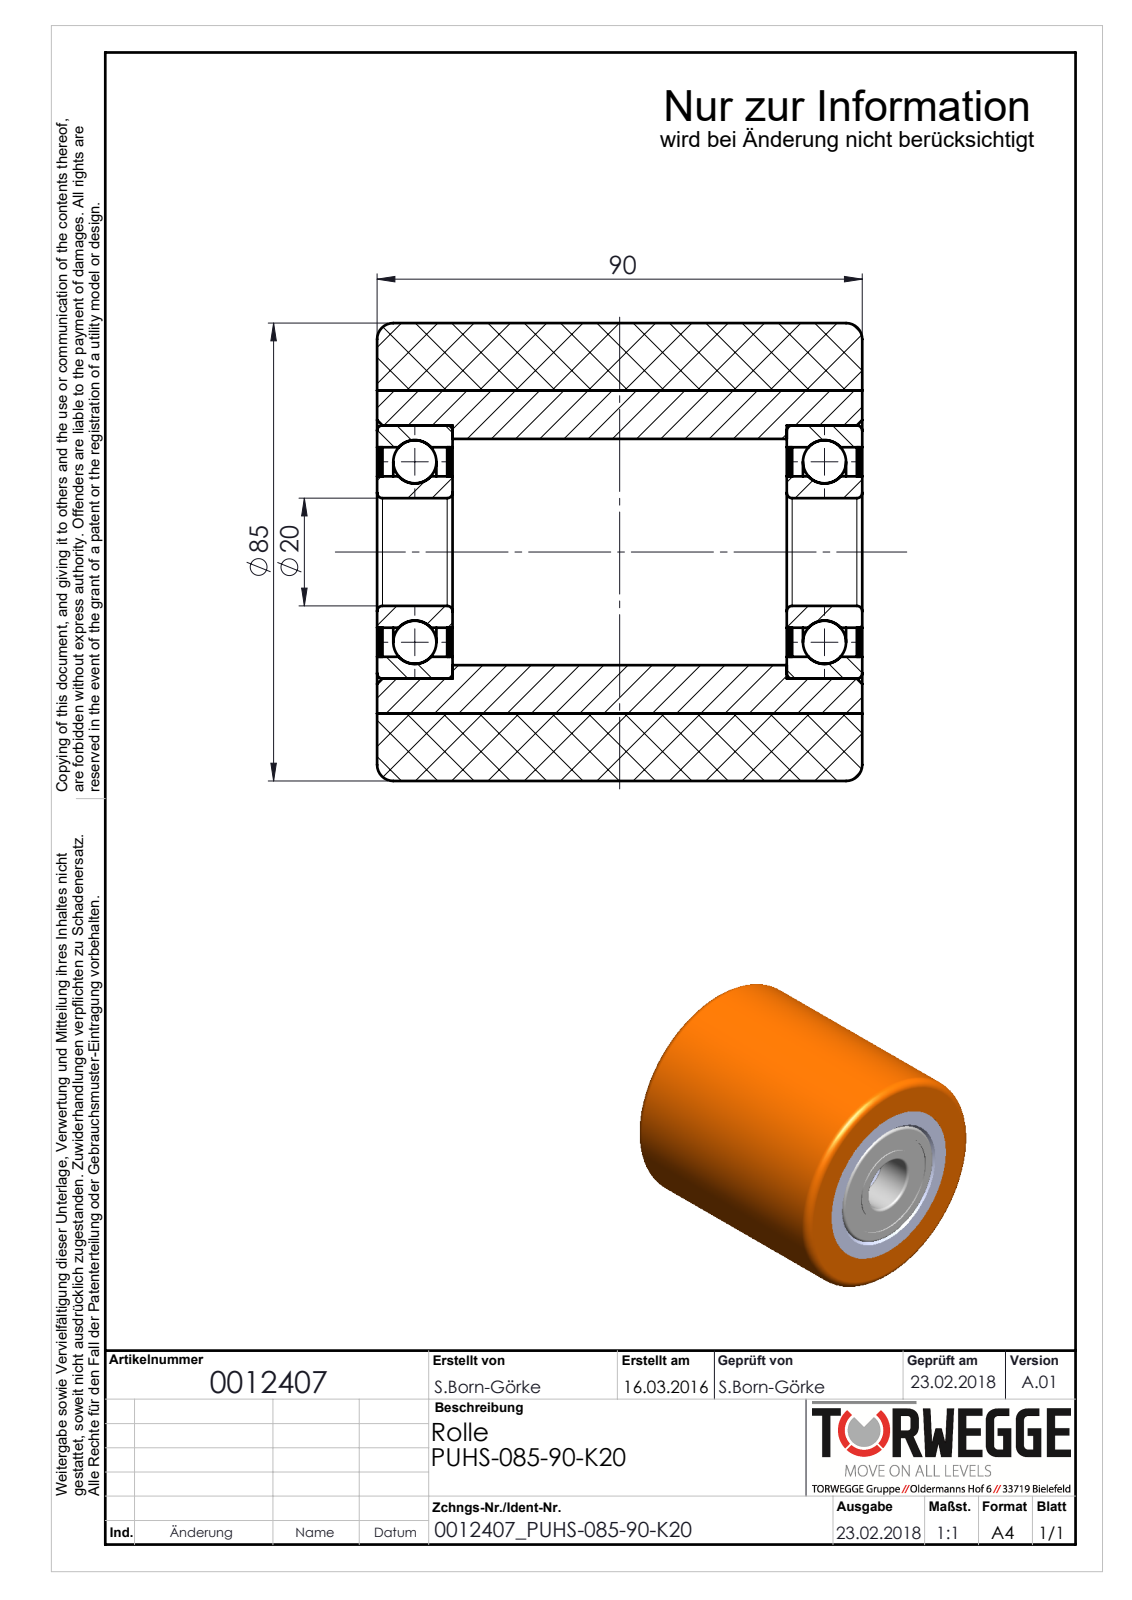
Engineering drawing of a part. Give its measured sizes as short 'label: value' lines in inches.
name: 0012407_PUHS-085-90-K20
written by: SolidWorks 2016 (AUTOMOTIVE_DESIGN)
unit: in
bodies: 12 solids, 118 faces (22 planar, 52 cylindrical, 44 other)
size: 3.543 × 3.346 × 3.346
volume: 24.89 in³; area: 160.3 in²
holes: 1× ⌀0.787, 1× ⌀1.106, 1× ⌀1.531, 1× ⌀1.654, 1× ⌀1.85, 1× ⌀2.362
bosses: 1× ⌀3.346
face distances: 0.02, 2.992, 3.543, 0.512, 0.039, 0.531, 3.012, 0.492, 2.972, 0.551
